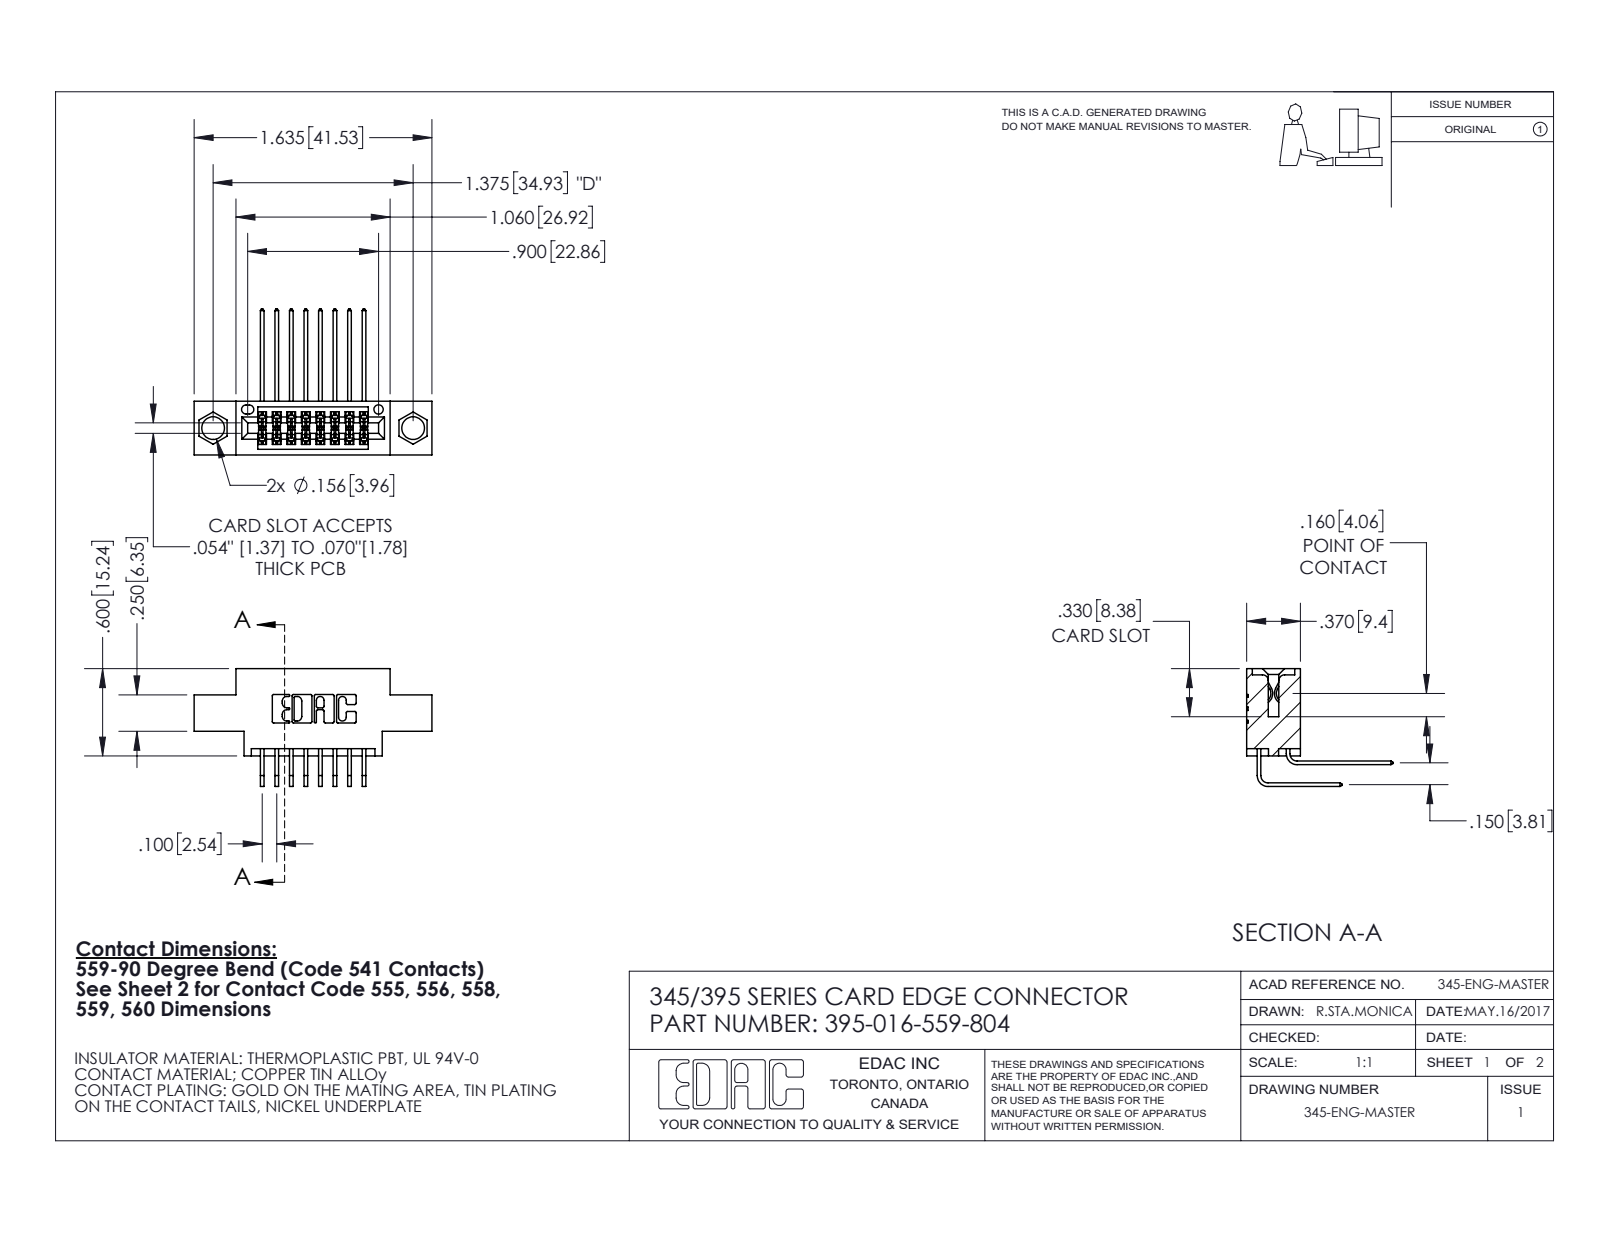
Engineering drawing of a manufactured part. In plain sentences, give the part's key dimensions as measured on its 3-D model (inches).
The part is named "345-292-001_558 559 Tail - 1; 345 Part_0.170 Offset - 0.156 Dia-TI; 395-016-559-804; 345-292-001_559 Tail - 2". Its 3-D file was written by "SolidWorks 2020 (CONFIG_CONTROL_DESIGN)". It is 17 solids with 976 faces: 658 planar, 318 cylindrical and 0 other. Overall it measures 1.635 by 1.005 by 0.809 inches. Its volume is 0.219 cubic inches and its surface area 7.873 square inches. Round holes: 2 of diameter 0.156, 1 of diameter 0.064. Partial cylindrical surfaces (rounded edges, fillets, slot ends): 24 of radius 0.006, 22 of radius 0.01, 6 of radius 0.007, 6 of radius 0.031, 3 of radius 0.026, 2 of radius 0.014, 2 of radius 0.019, 2 of radius 0.022. The main face-to-face distances are 0.2, 0.37, 0.072, 0.298, 0.1, 0.15, 0.098, 0.272, 0.025, 0.175. The hole center spacings are 0.27, 1.144, 1.375.
